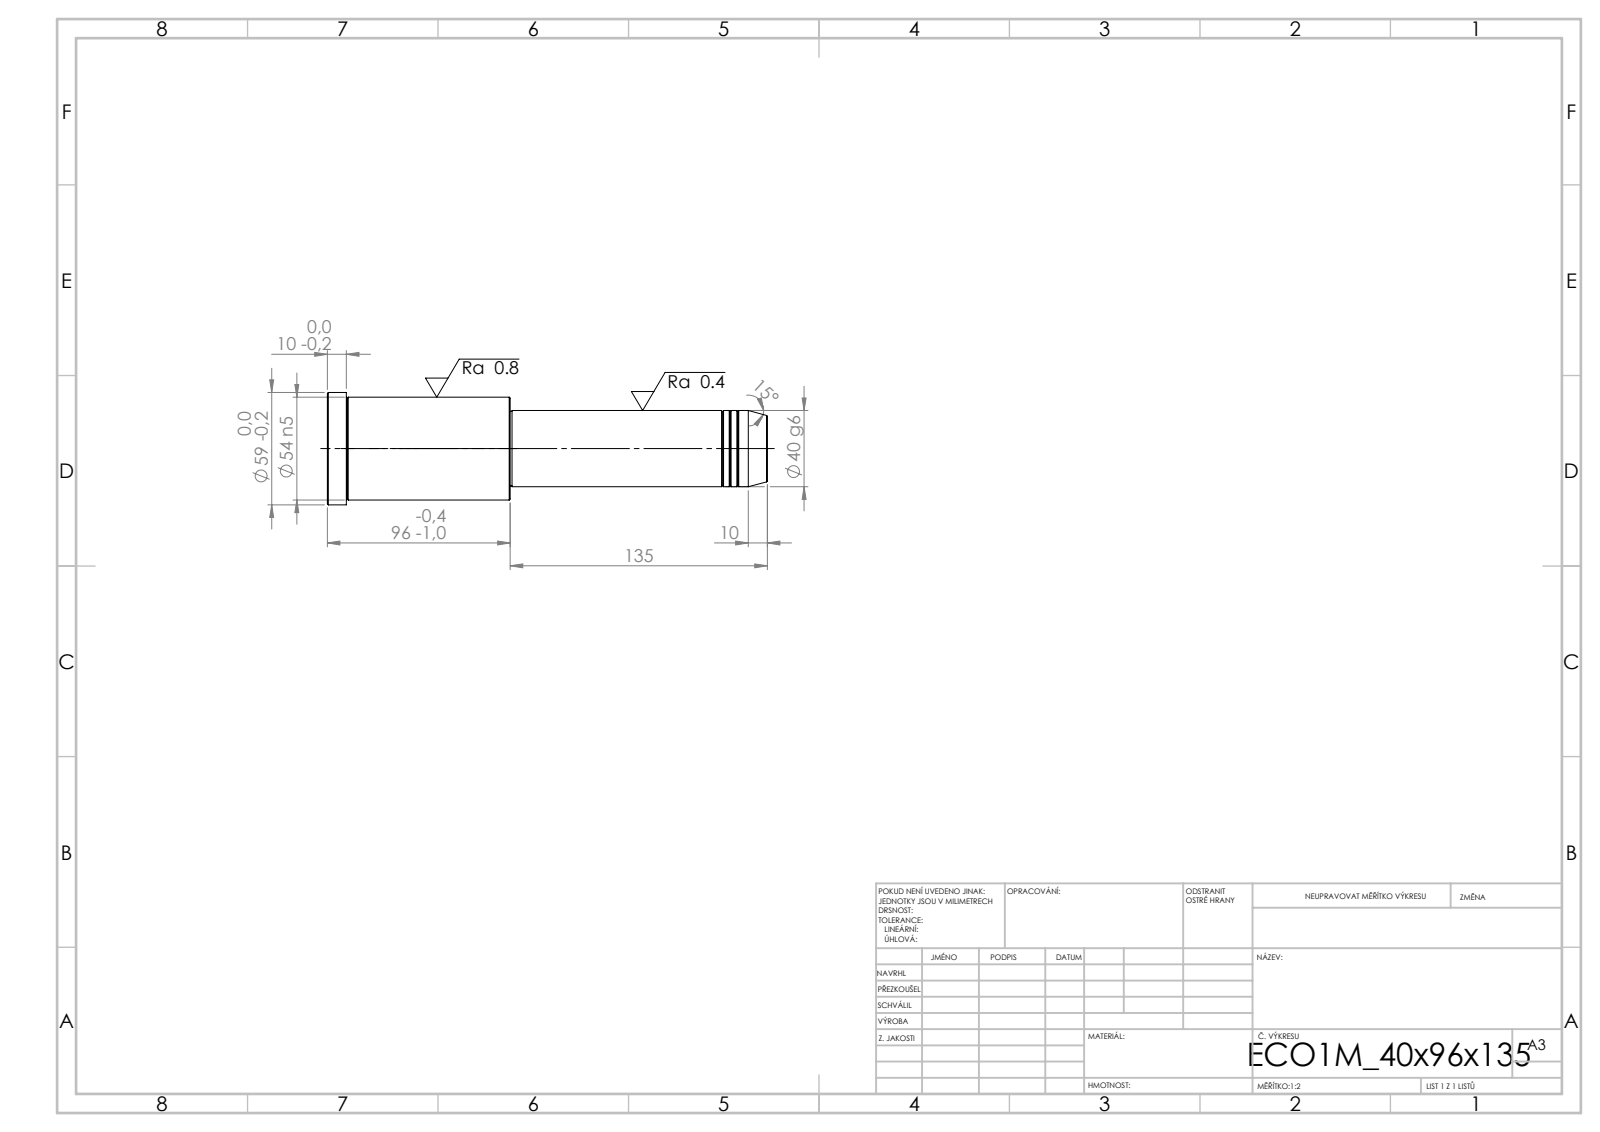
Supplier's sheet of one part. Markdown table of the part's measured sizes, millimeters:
| quantity | value |
| --- | --- |
| STEP written by | SolidWorks 2019 (CONFIG_CONTROL_DESIGN) |
| units | millimeters |
| bodies | 1 solid, 43 faces (5 planar, 14 cylindrical, 24 other) |
| overall size | 231 × 59 × 59 |
| volume | 392 015 mm³ |
| surface area | 38 822 mm² |
| round bosses / shafts (diameter × count) | 59 × 1, 54 × 1, 40 × 1, 39 × 1 |
| main face-to-face distances | 96, 135, 231, 221, 86, 10, 134, 1, 87, 97 |
